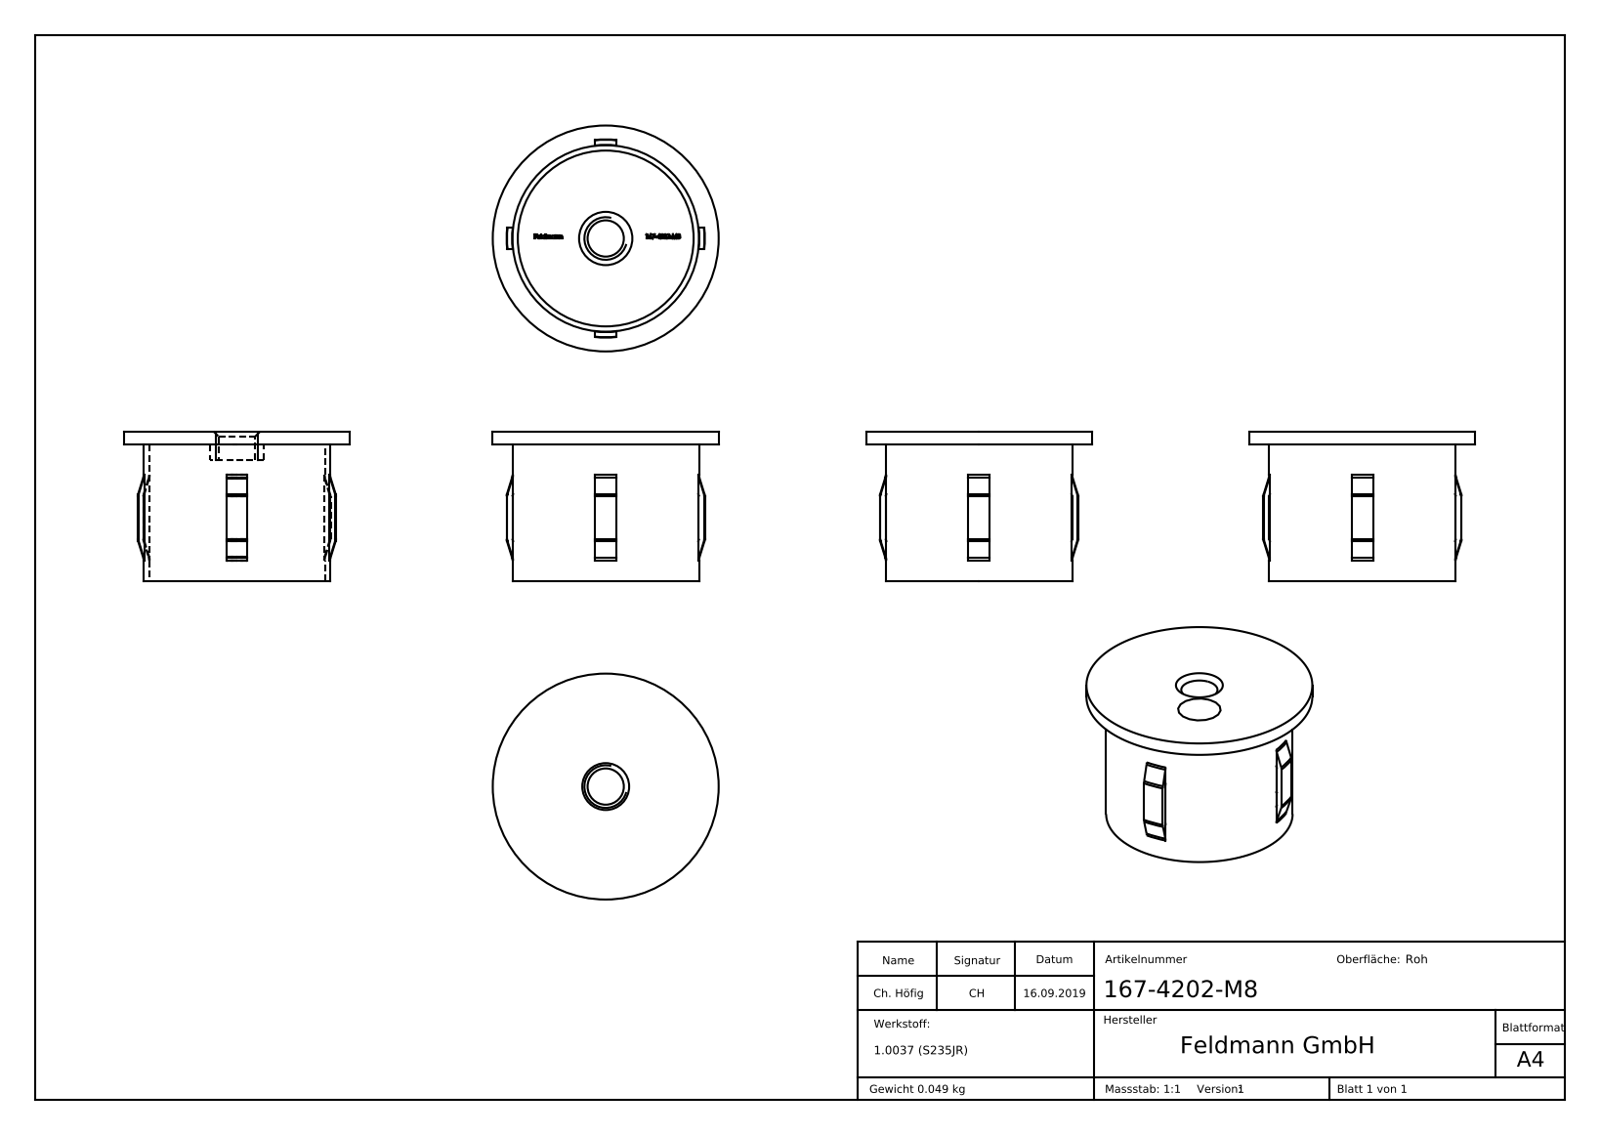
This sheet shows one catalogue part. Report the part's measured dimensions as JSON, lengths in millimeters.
{"part_name": "167-4202-M8", "step_written_by": "SolidWorks 2015 (CONFIG_CONTROL_DESIGN)", "units": "millimeters", "bodies": {"solids": 1, "faces": 340, "planar": 163, "cylindrical": 20, "other": 157}, "overall_size": [42.4, 42.4, 28.2], "volume_mm3": 6296, "surface_area_mm2": 8977, "round_holes": [[6.8, 1], [33, 1]], "round_bosses_or_shafts": [[42.4, 1], [35, 1], [10, 1]], "partial_cylinders_radius": [[17.6, 1], [18.6, 1]], "face_to_face_distances": [2.5, 25.7, 28.2, 4, 22.9, 2.8, 5.3, 2.4, 25.8, 2.9]}
